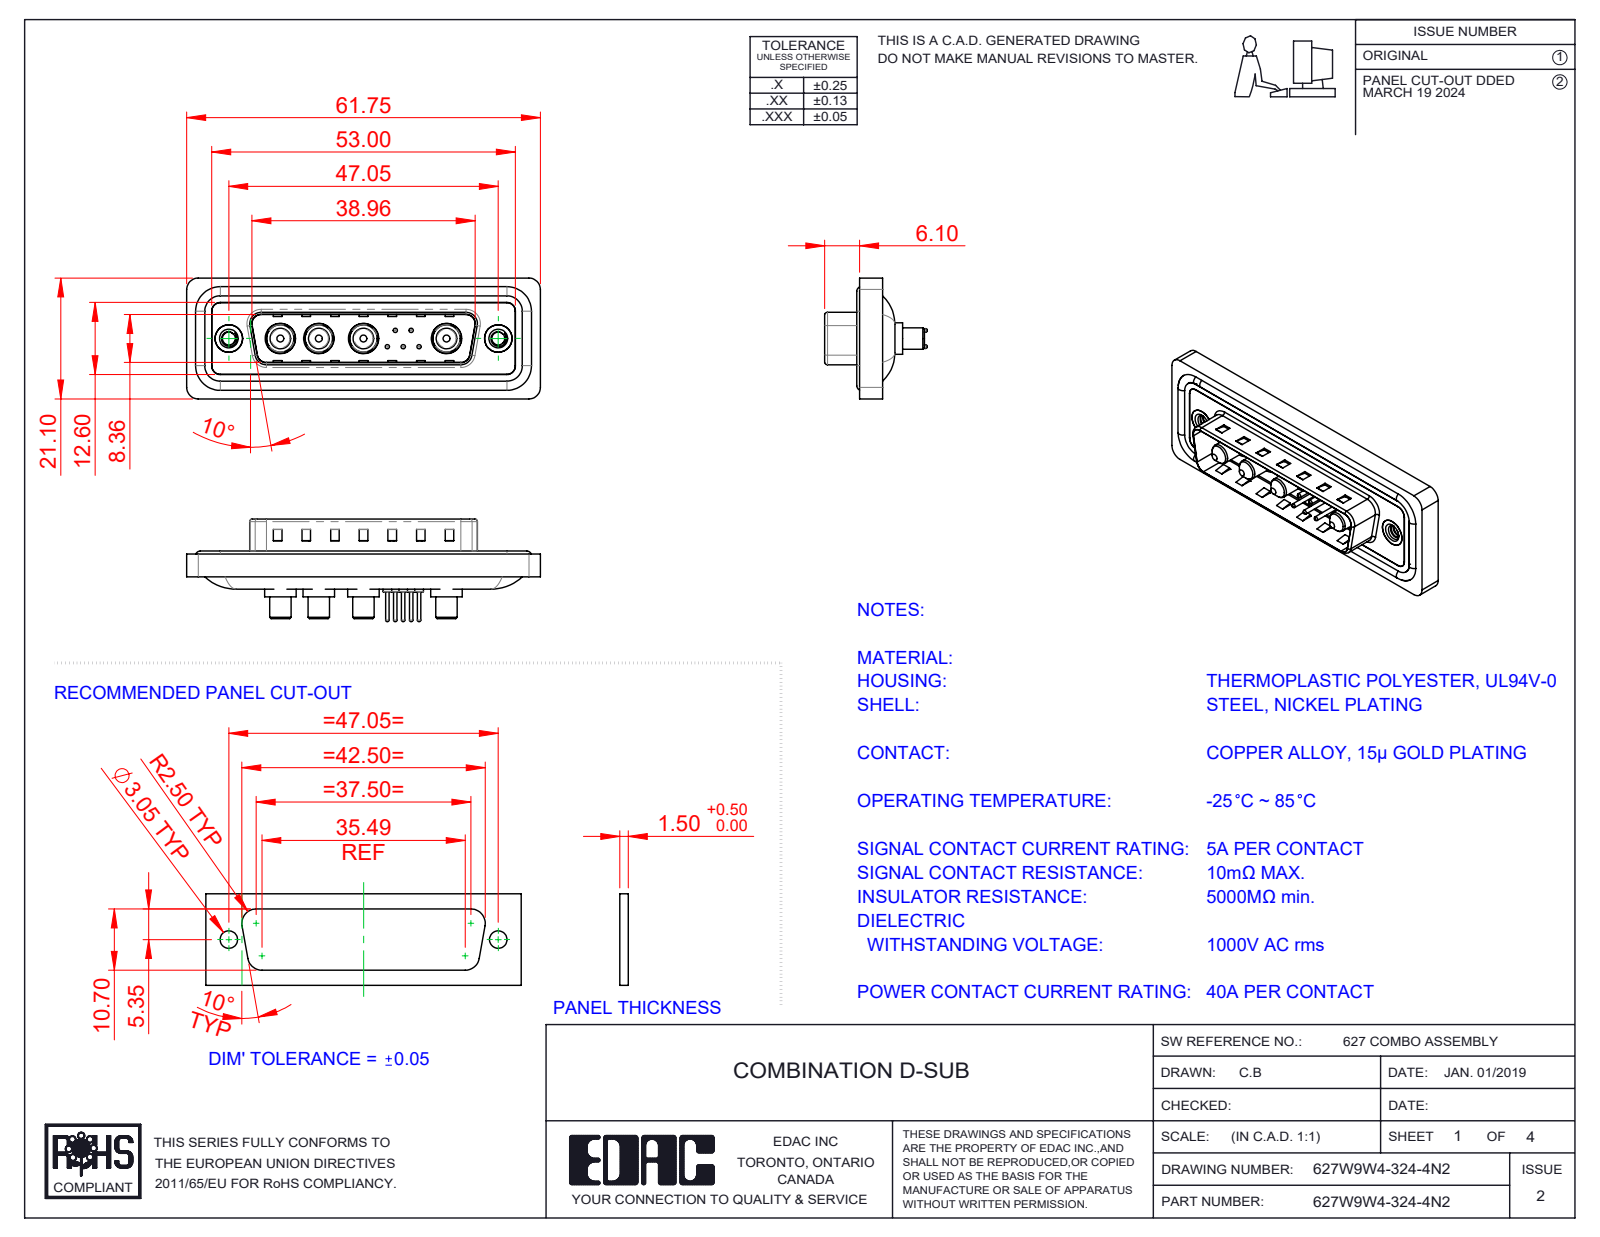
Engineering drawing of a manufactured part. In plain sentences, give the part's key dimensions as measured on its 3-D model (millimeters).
The part is named "627Combo Shell Front_25 Contacts; 627Combo Waterproof Housing_25 Contacts; 627W9W4-324-4N2; 627Combo Contact Row 1_24 (+5 more)". Its 3-D file was written by "SolidWorks 2023 (CONFIG_CONTROL_DESIGN)". It is 20 solids with 824 faces: 284 planar, 334 cylindrical and 206 other. Overall it measures 61.75 by 21.1 by 17.9 millimeters. Its volume is 7 478 cubic millimeters and its surface area 11 879 square millimeters. Round holes: 5 of diameter 0.75, 5 of diameter 1.6, 5 of diameter 2, 4 of diameter 4.85, 4 of diameter 5.3, 2 of diameter 2.26, 2 of diameter 4, 2 of diameter 4.8, 2 of diameter 5. Round bosses or shafts: 5 of diameter 1.5, 5 of diameter 0.6, 4 of diameter 5.5, 4 of diameter 5.2, 4 of diameter 4.75, 4 of diameter 3.75, 4 of diameter 3.6, 4 of diameter 1.6. Partial cylindrical surfaces (rounded edges, fillets, slot ends): 22 of radius 1.5, 18 of radius 2, 8 of radius 0.5, 8 of radius 1.6, 4 of radius 0.25, 4 of radius 0.6, 4 of radius 0.65, 4 of radius 0.9. The main face-to-face distances are 0.4, 1.5, 1.1, 0.5, 1.6, 3.1, 2.9, 0.82, 9.58, 5.65. The hole center spacings are 3.16, 2.77, 5.04, 14.51, 2.78, 4.4, 4.41, 5.
